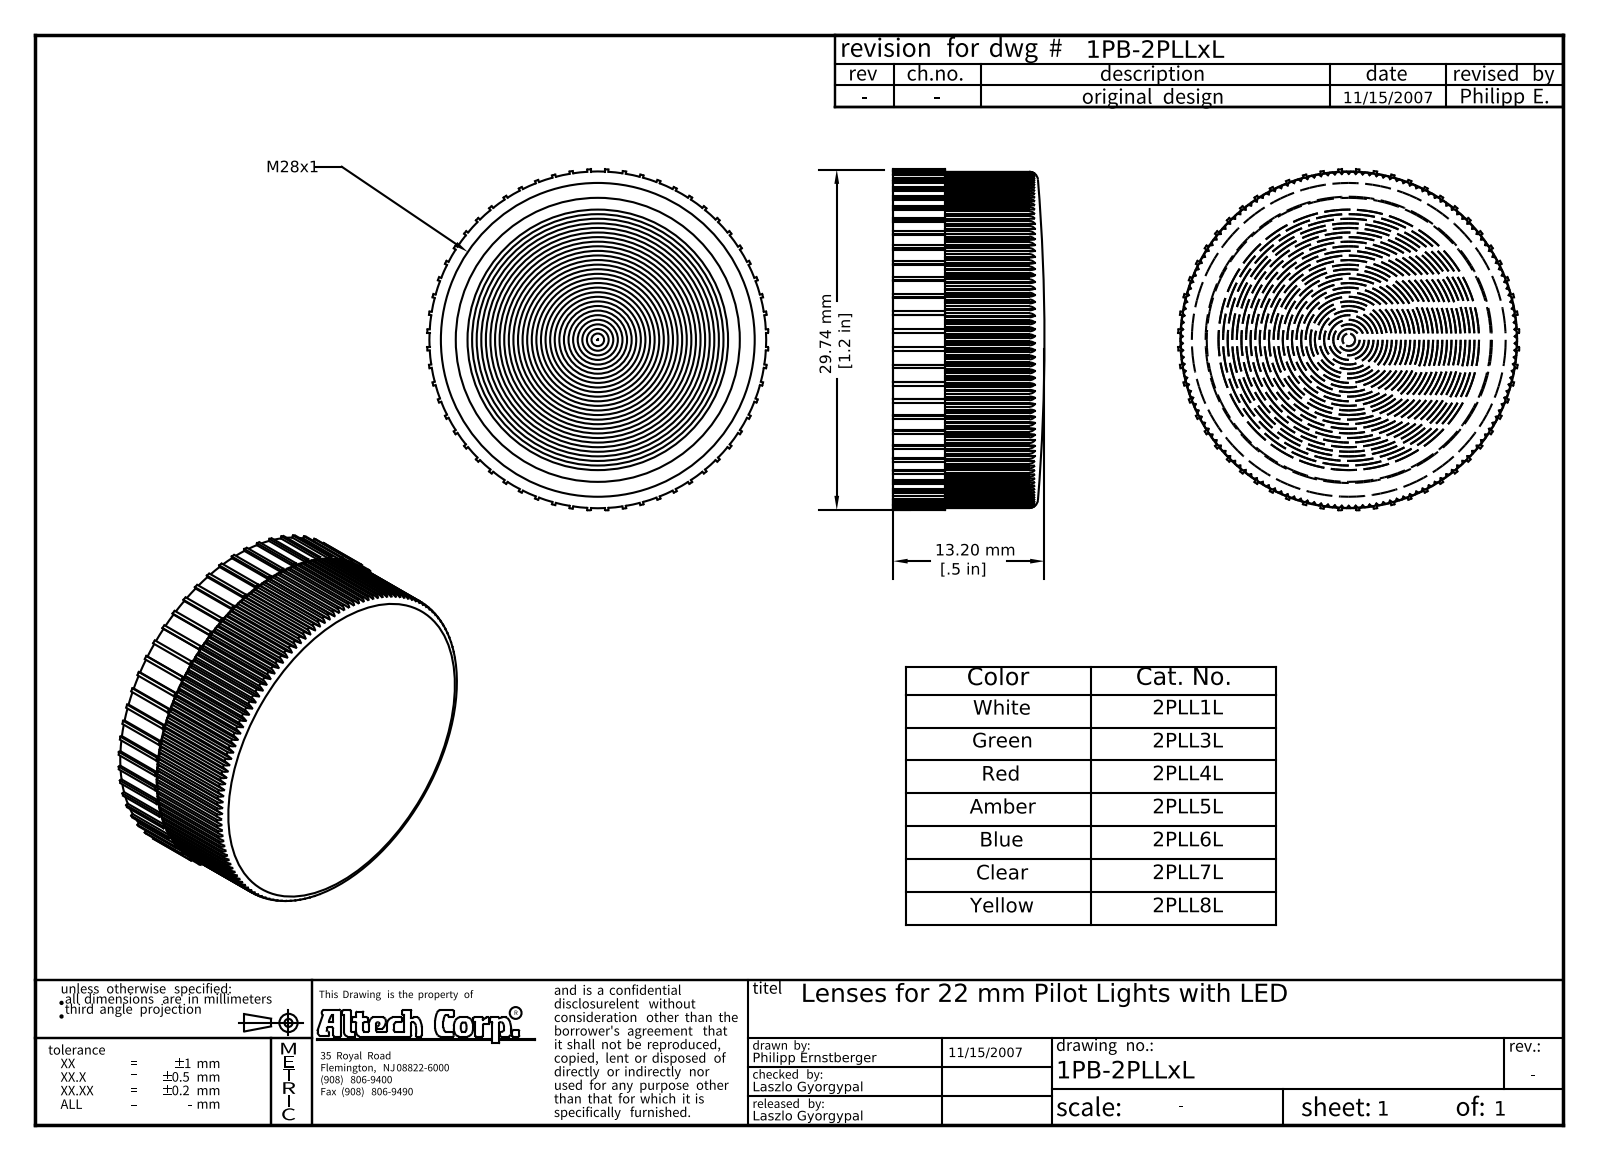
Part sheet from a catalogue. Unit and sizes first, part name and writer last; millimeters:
Units: millimetres
Overall size (bounding box): 29.77 × 29.77 × 13.2
Round holes (diameter × count): ⌀25 ×1, ⌀27.4 ×1
Round bosses / shafts (diameter × count): ⌀29.4 ×1
Partial cylindrical surfaces — rounded edges, fillets, slot ends (radius × count): R14.68 ×1, R14.9 ×1
Main face-to-face distances: 20.5, 20.51, 3.8, 1.25, 20.52, 20.49, 4.5, 0.7, 20.53, 1.26
Volume: 2 597 mm³ · Surface area: 4 221 mm²
Bodies: 2 solids, 727 faces (423 planar, 272 cylindrical, 32 other)
Part name (STEP PRODUCT): 2PLLxL; lense; rubber
STEP written by: Autodesk Inventor 2008 (AUTOMOTIVE_DESIGN)
